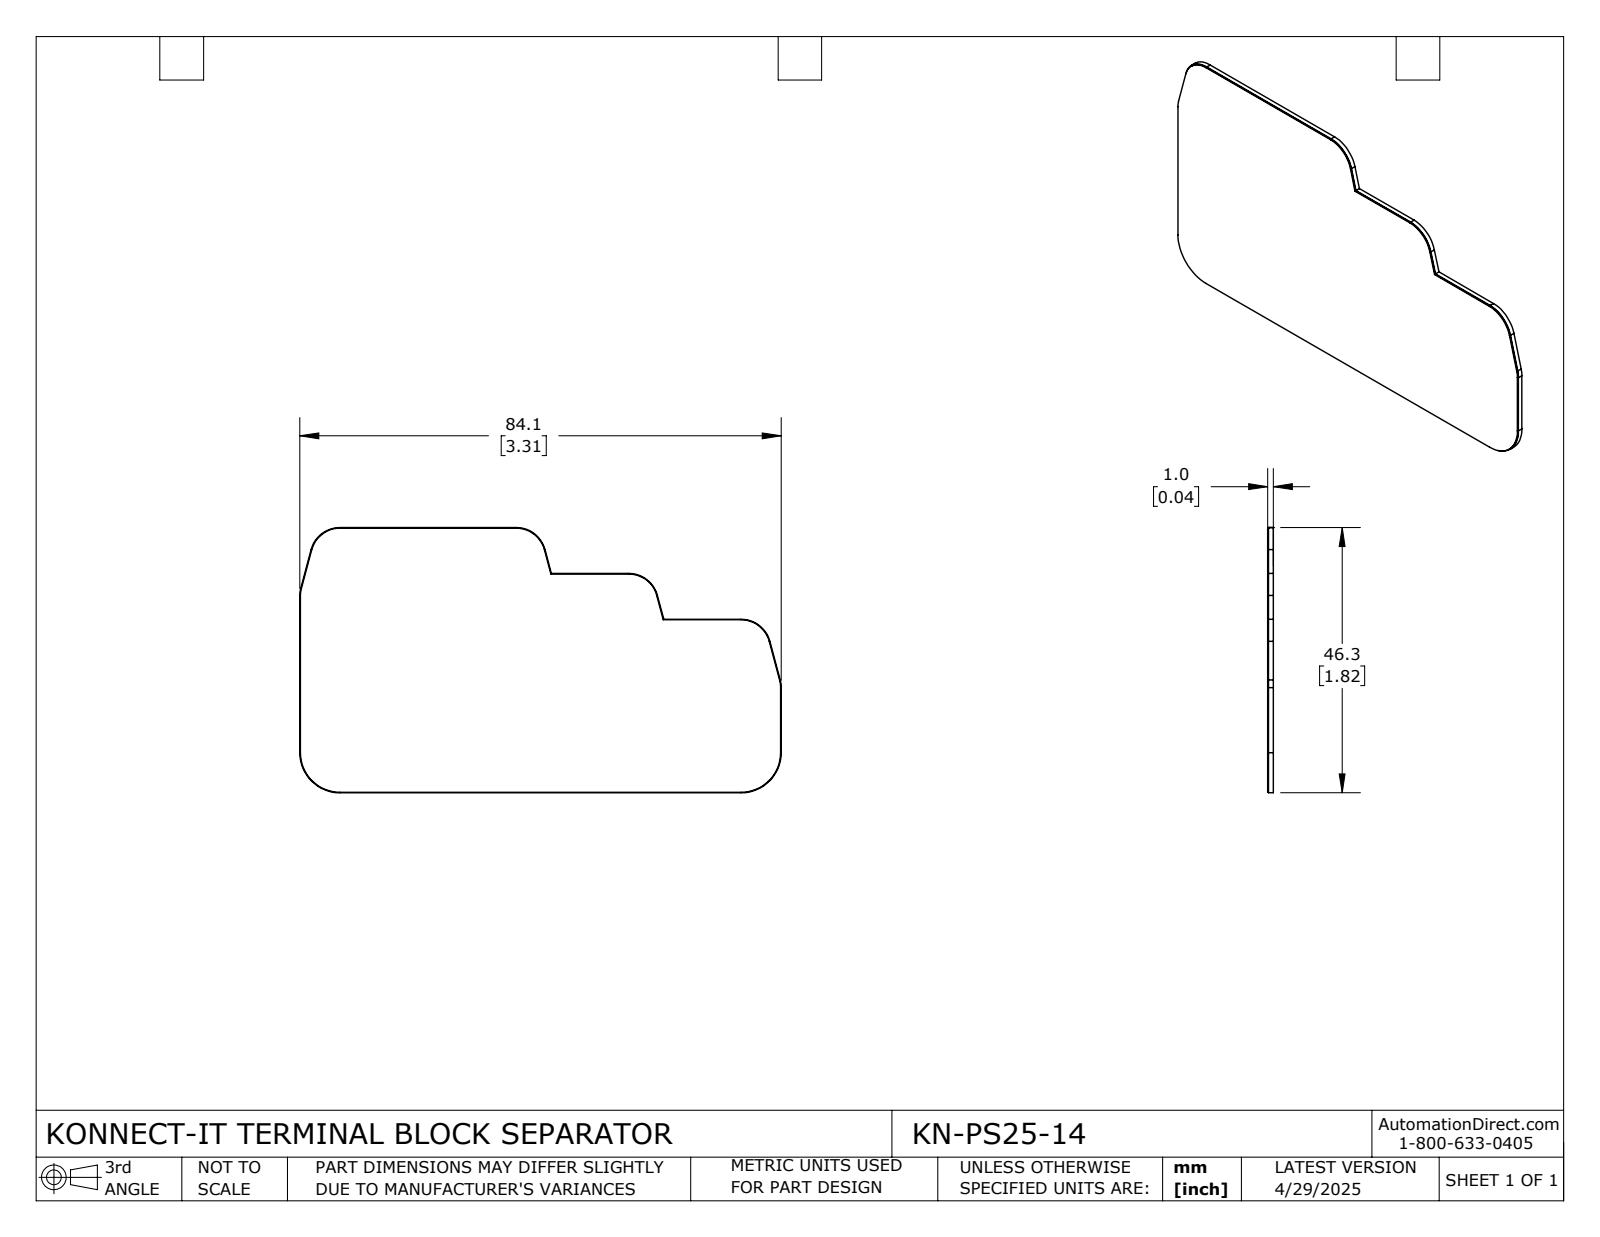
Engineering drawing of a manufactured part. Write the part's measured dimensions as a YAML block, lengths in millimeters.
part_name: "KN-PS25-14"
step_written_by: "SolidWorks 2024 (CONFIG_CONTROL_DESIGN)"
units: millimeters
bodies: {solids: 1, faces: 39, planar: 23, cylindrical: 16, other: 0}
overall_size: [84.05, 46.3, 1]
volume: 3319
surface_area: 6886
partial_cylinders:
  - {radius: 5.1, count: 6}
  - {radius: 5.2, count: 6}
  - {radius: 6.9, count: 2}
  - {radius: 7, count: 2}
face_to_face_distances: [1, 8, 46.3, 0.85, 46.2, 16, 30.2, 38.2, 30.3, 38.3]
